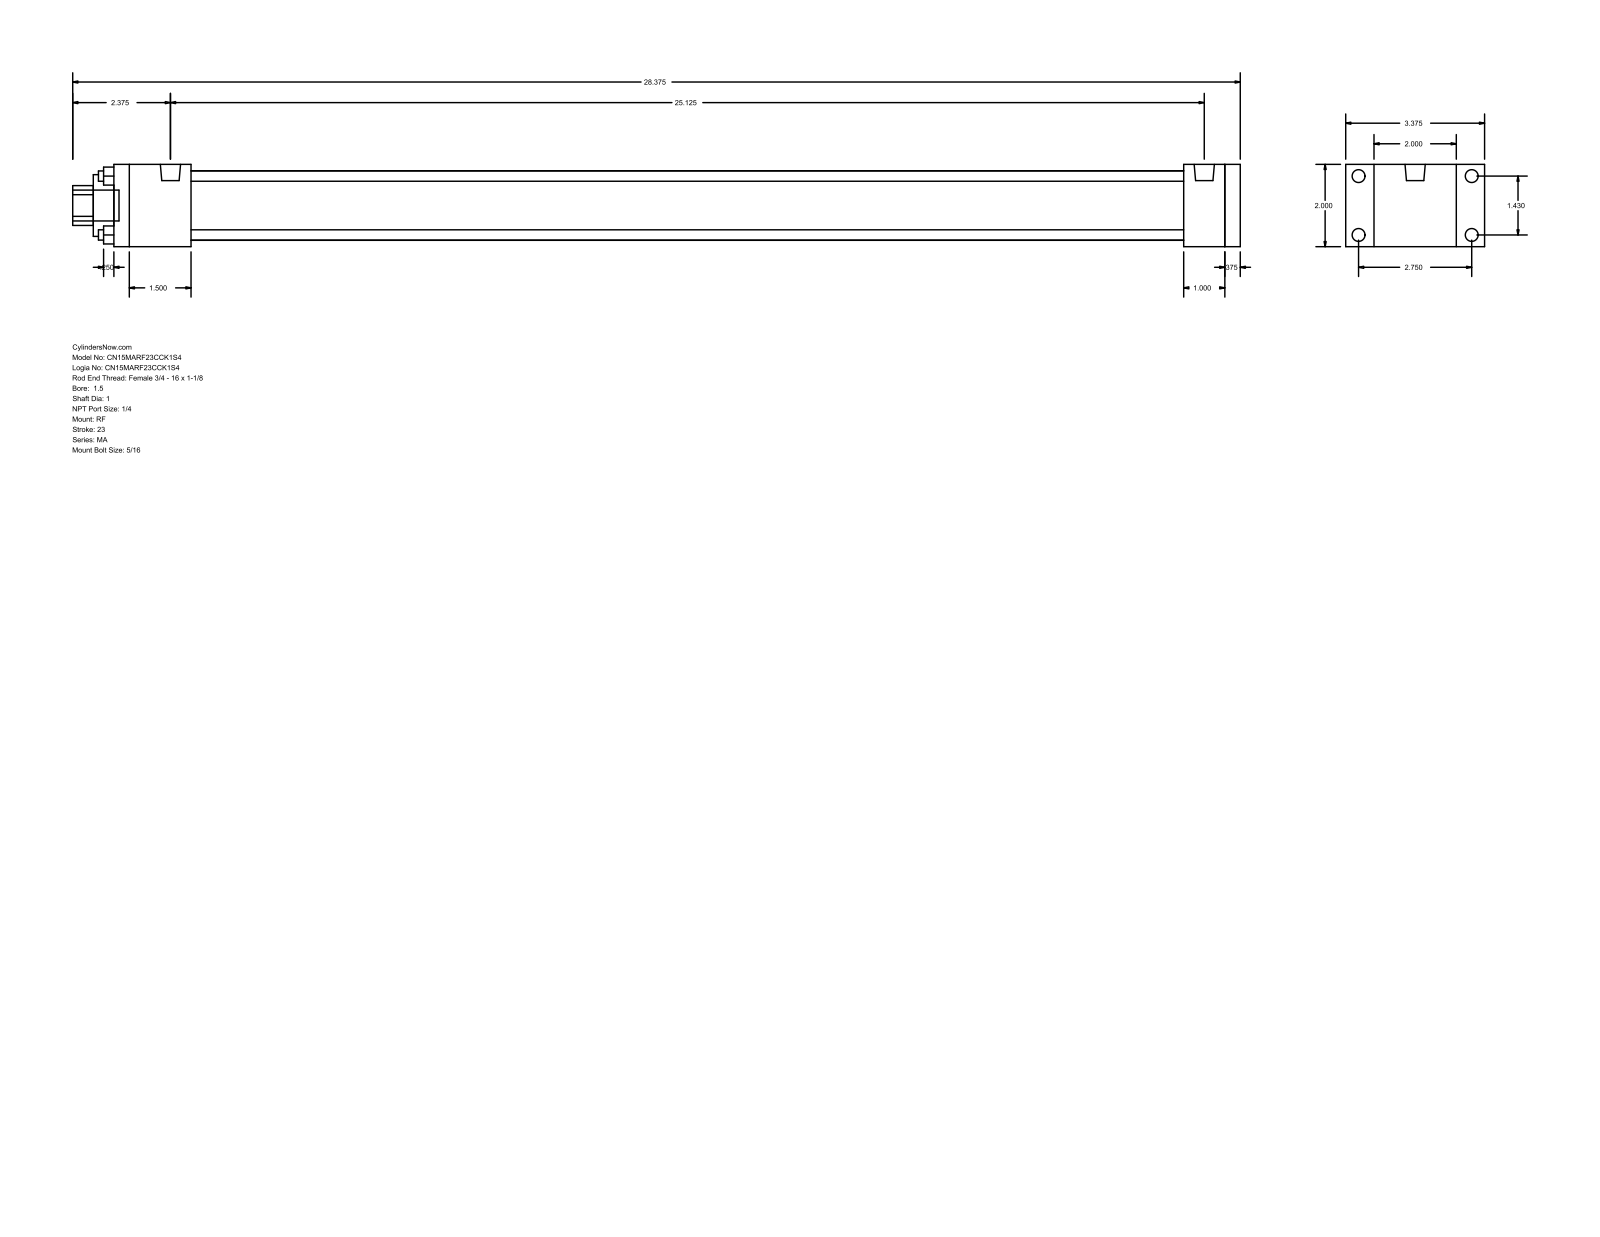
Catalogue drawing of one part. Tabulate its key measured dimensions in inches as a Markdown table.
| quantity | value |
| --- | --- |
| part name | MA_RF__0150_1 |
| STEP written by | GSSL Pune (CONFIG_CONTROL_DESIGN) |
| units | inches |
| bodies | 0 solids, 92 faces (64 planar, 28 cylindrical, 0 other) |
| overall size | 28.375 × 3.375 × 2 |
| round holes (diameter × count) | 0.25 × 4, 1 × 1, 1.5 × 1, 1.69 × 1 |
| round bosses / shafts (diameter × count) | 0.313 × 8, 0.492 × 2, 0.75 × 1 |
| partial cylindrical surfaces (radius × count) | 0.484 × 1 |
| main face-to-face distances | 2, 0.375, 27, 1, 27.375, 26, 1.375, 1.875, 24.125, 25.125 |
| hole center spacings | 1.011, 1.43, 2.022 |
